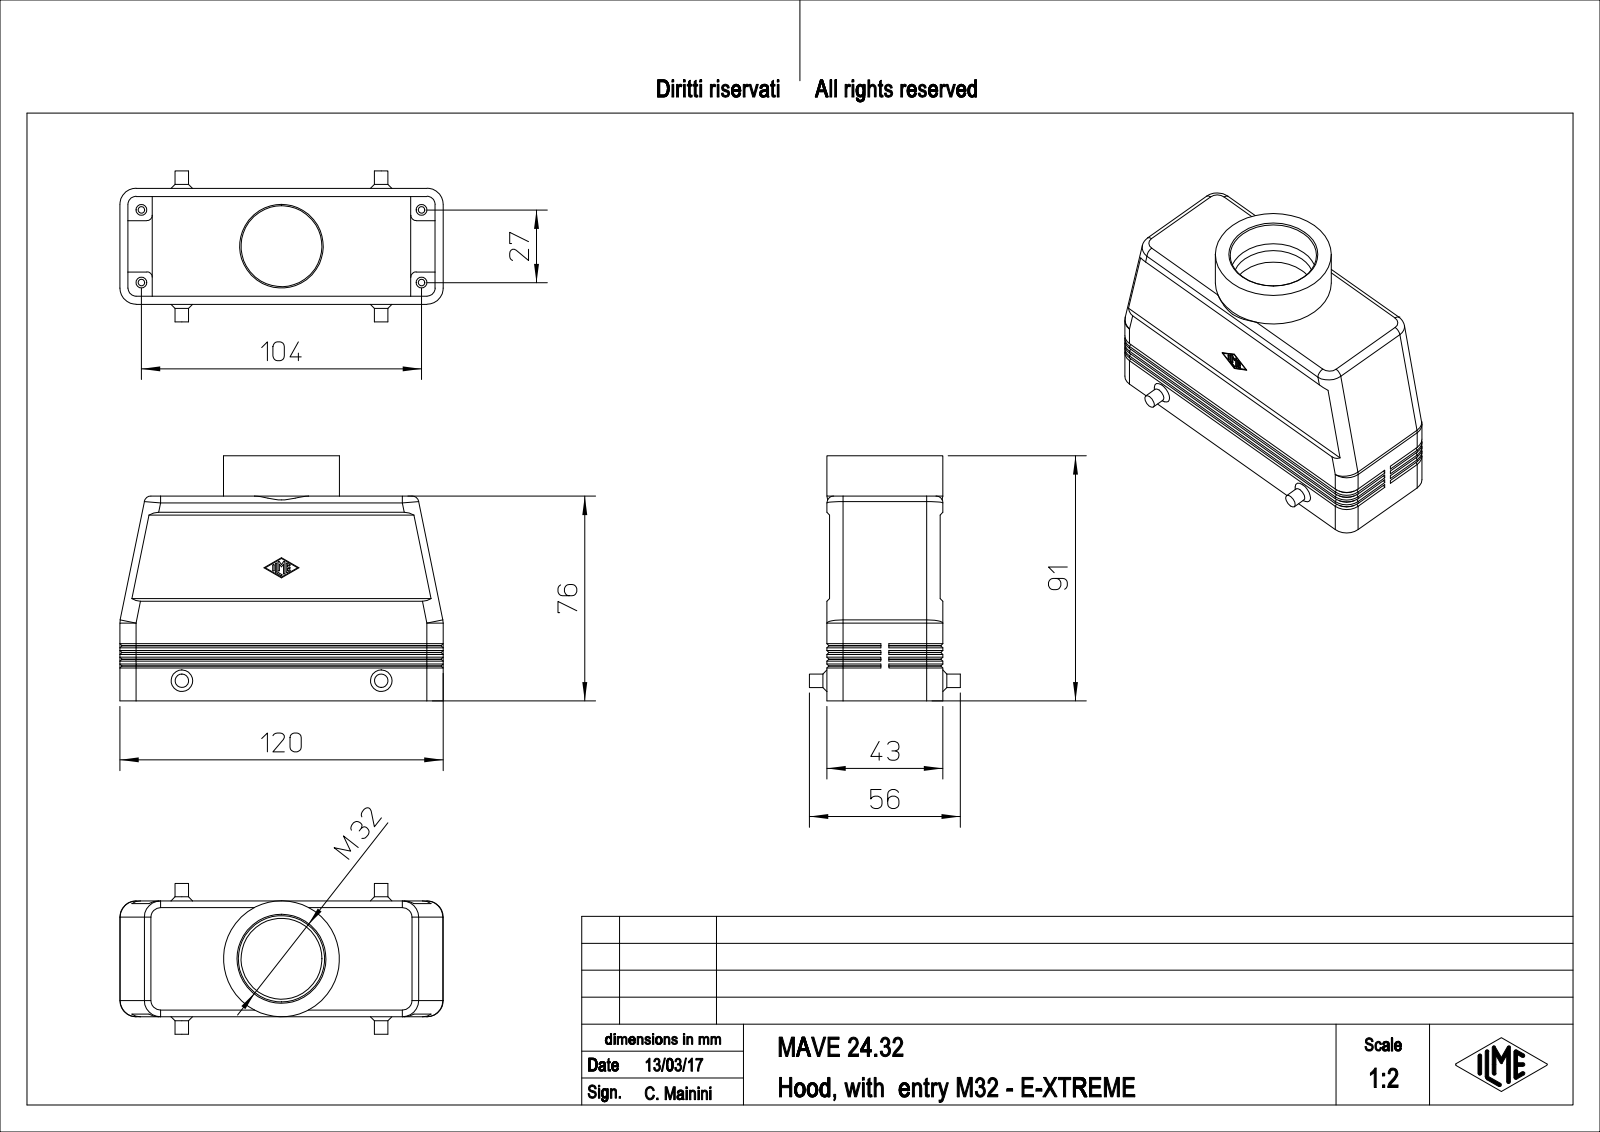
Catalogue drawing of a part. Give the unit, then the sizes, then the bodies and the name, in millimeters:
Units: millimetres
Overall size (bounding box): 120 × 91 × 56
Round holes (diameter × count): ⌀2.46 ×4, ⌀4 ×4, ⌀30 ×1, ⌀32 ×1
Round bosses / shafts (diameter × count): ⌀5 ×2, ⌀43 ×1, ⌀31 ×1
Partial cylindrical surfaces — rounded edges, fillets, slot ends (radius × count): R0.25 ×14, R6 ×10, R2 ×4, R2.5 ×4, R3 ×4, R5.3 ×4
Main face-to-face distances: 3, 37, 40, 1, 2, 42, 39, 43, 41, 12
Hole centre spacings: 53.72, 27, 104, 107.45
Volume: 92 696 mm³ · Surface area: 57 038 mm²
Bodies: 1 solid, 341 faces (179 planar, 100 cylindrical, 62 other)
Part name (STEP PRODUCT): MAVE_24.32
STEP written by: PTC Creo Elements/Direct Modeling 19.0E 27-Jun-2016 (C) Parametric Technology GmbH (AUTOMOTIVE_DESIGN)
